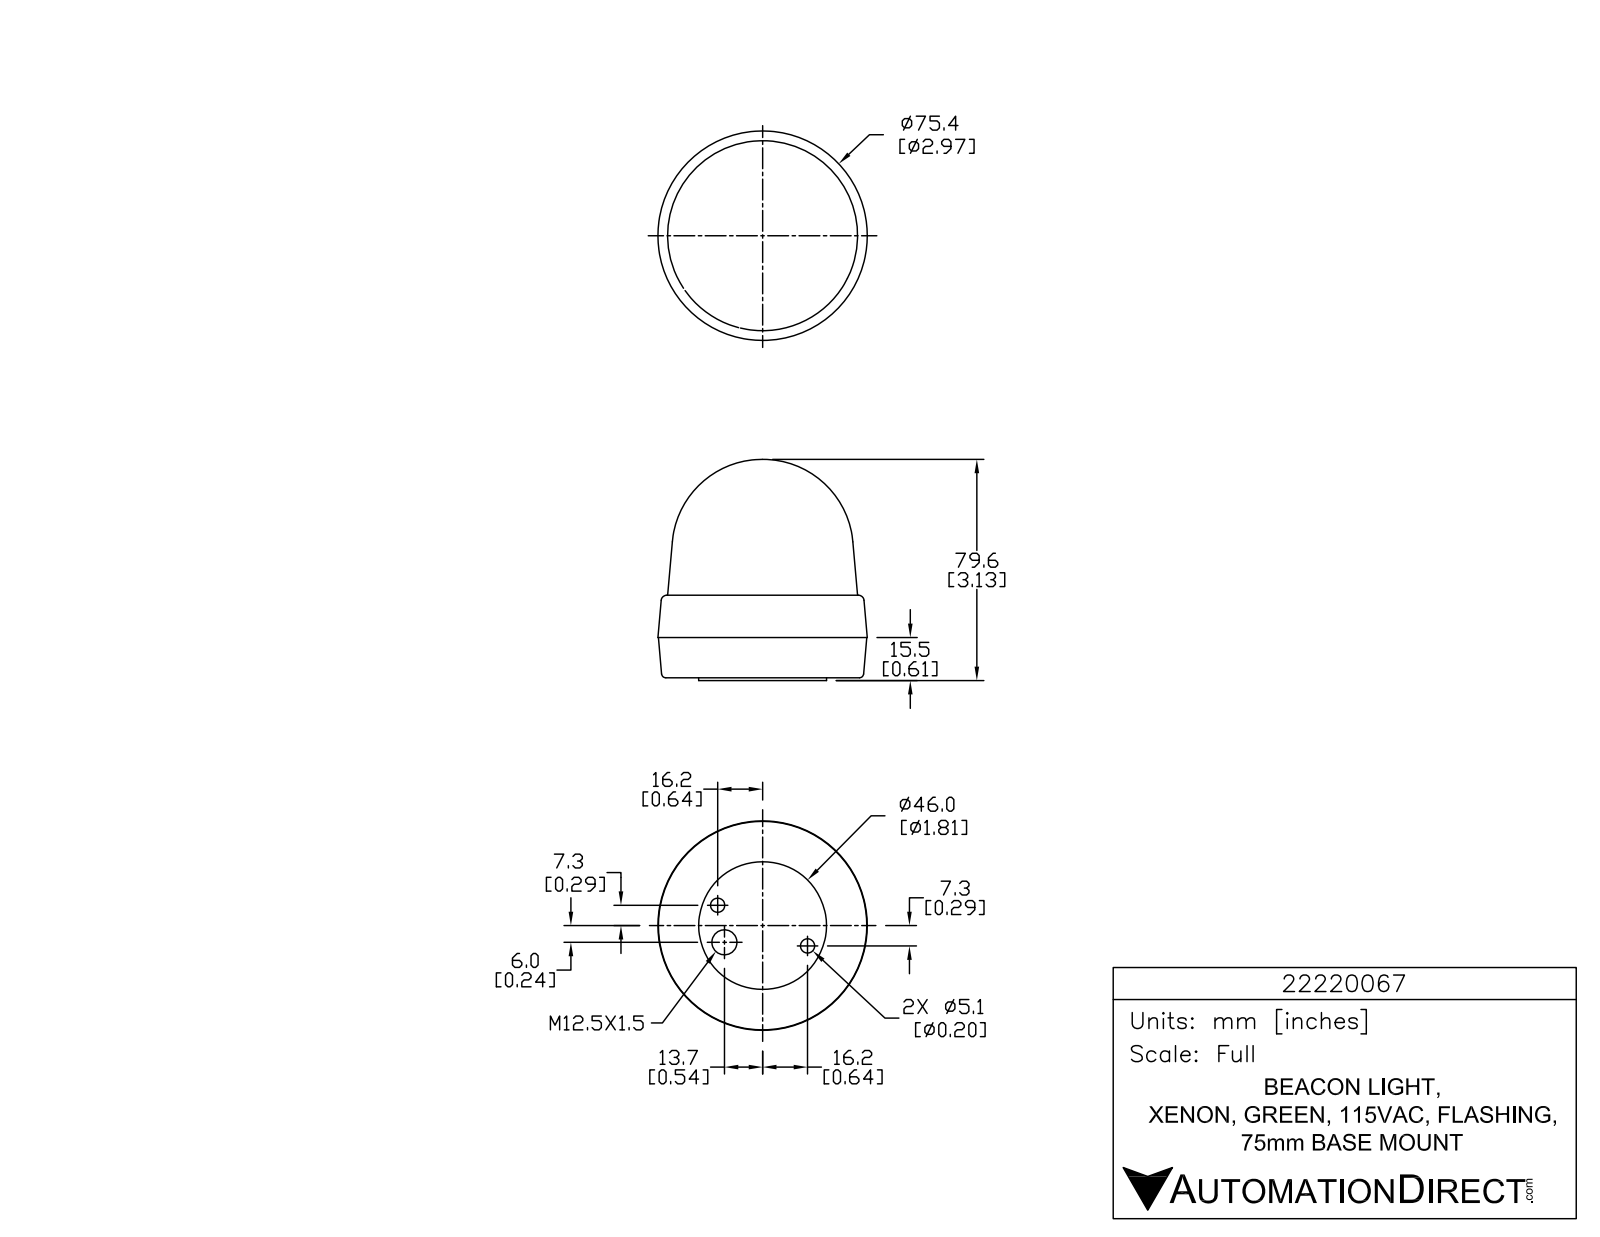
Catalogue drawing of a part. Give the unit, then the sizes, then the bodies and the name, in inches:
Units: inches
Overall size (bounding box): 3.133 × 2.967 × 2.967
Round holes (diameter × count): ⌀0.059 ×3, ⌀0.201 ×2, ⌀0.354 ×1
Round bosses / shafts (diameter × count): ⌀0.339 ×3, ⌀0.084 ×3, ⌀1.811 ×1
Partial cylindrical surfaces — rounded edges, fillets, slot ends (radius × count): R0.005 ×9, R0.005 ×6, R0.012 ×6, R0.012 ×6, R0.012 ×6, R0.196 ×6, R0.005 ×3, R0.005 ×3
Main face-to-face distances: 0.039, 1.209, 1.17, 0.61, 0.571, 0.599, 1.566, 1.527, 0.956, 0.357
Hole centre spacings: 0.534, 1.179, 1.398
Volume: 15.79 in³ · Surface area: 33.7 in²
Bodies: 1 solid, 773 faces (526 planar, 163 cylindrical, 84 other)
Part name (STEP PRODUCT): 22220067
STEP written by: SolidWorks 2015 (AUTOMOTIVE_DESIGN)
